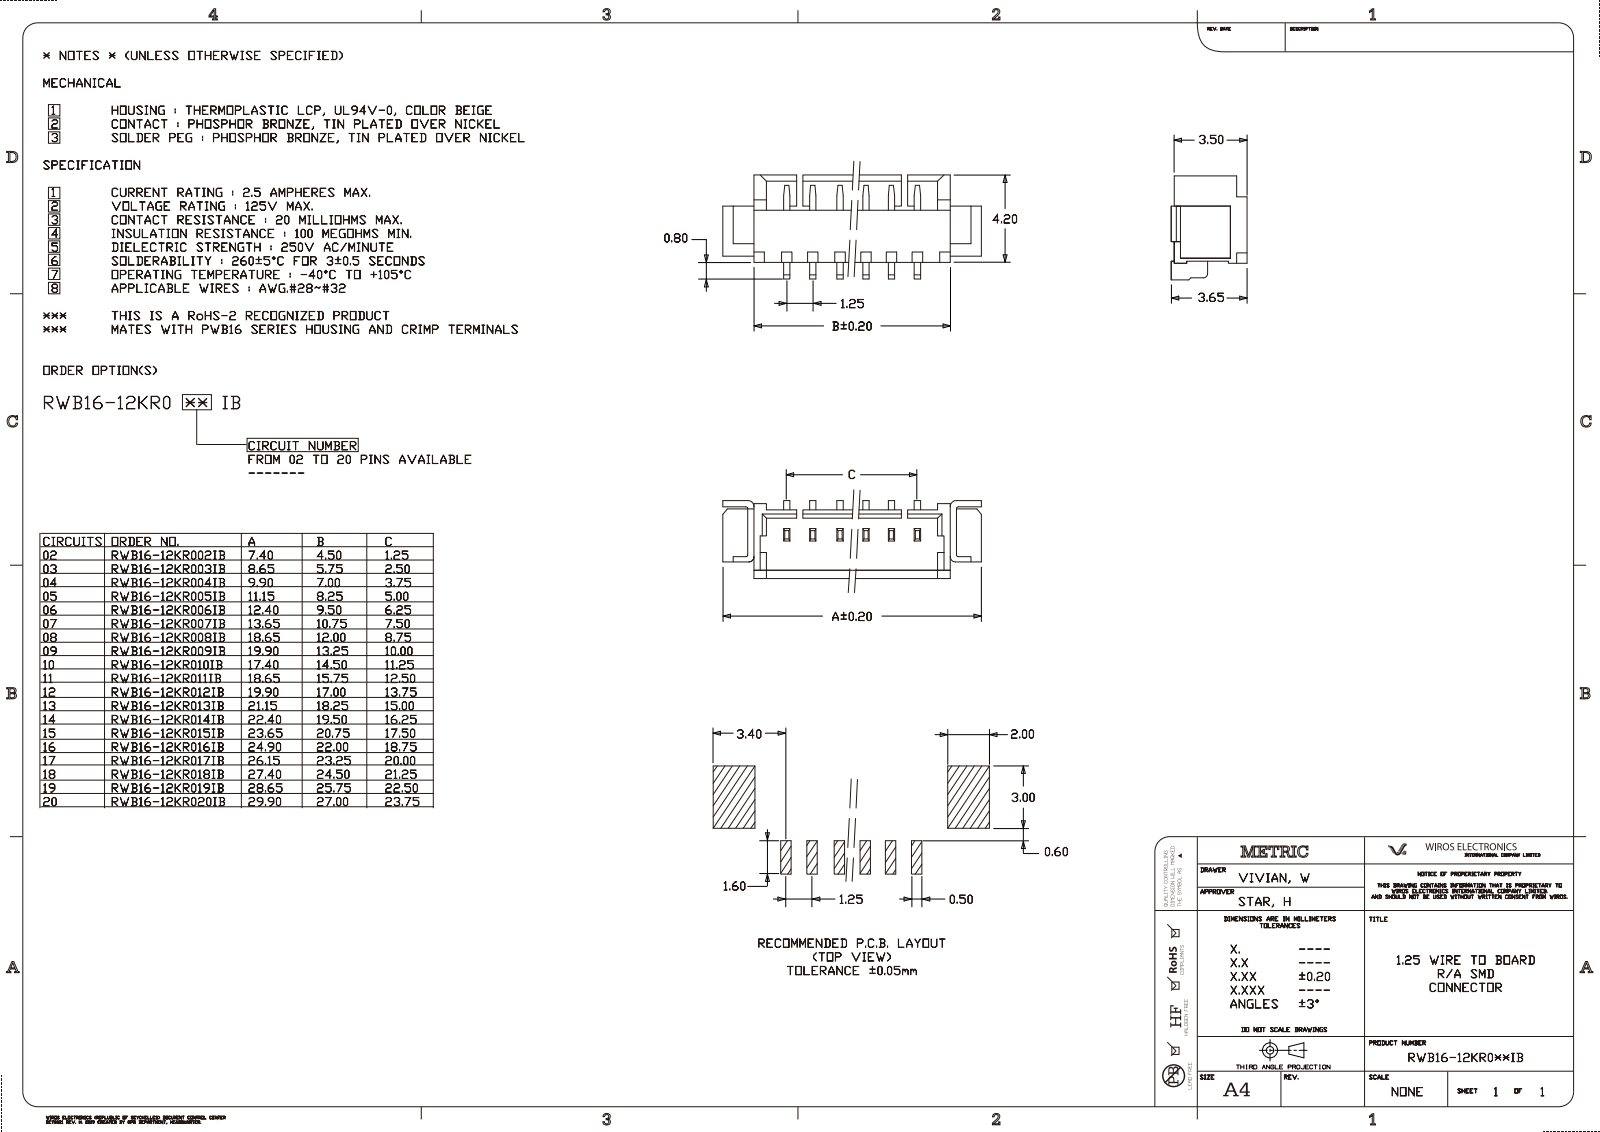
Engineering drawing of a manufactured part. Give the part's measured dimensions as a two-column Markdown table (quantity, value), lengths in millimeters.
| quantity | value |
| --- | --- |
| part name | Admi81DD0wog |
| STEP written by | UGS - NX 4.0 (AUTOMOTIVE_DESIGN) |
| units | millimeters |
| bodies | 1 solid, 368 faces (260 planar, 100 cylindrical, 8 other) |
| overall size | 10.35 × 5.1 × 3.45 |
| volume | 80 mm³ |
| surface area | 295 mm² |
| partial cylindrical surfaces (radius × count) | 0.2 × 16, 0.15 × 15, 0.1 × 4, 0.35 × 4 |
| main face-to-face distances | 1.25, 3.2, 2.82, 0.38, 2.8, 3.45, 2.5, 1.75, 3.07, 1.55 |
